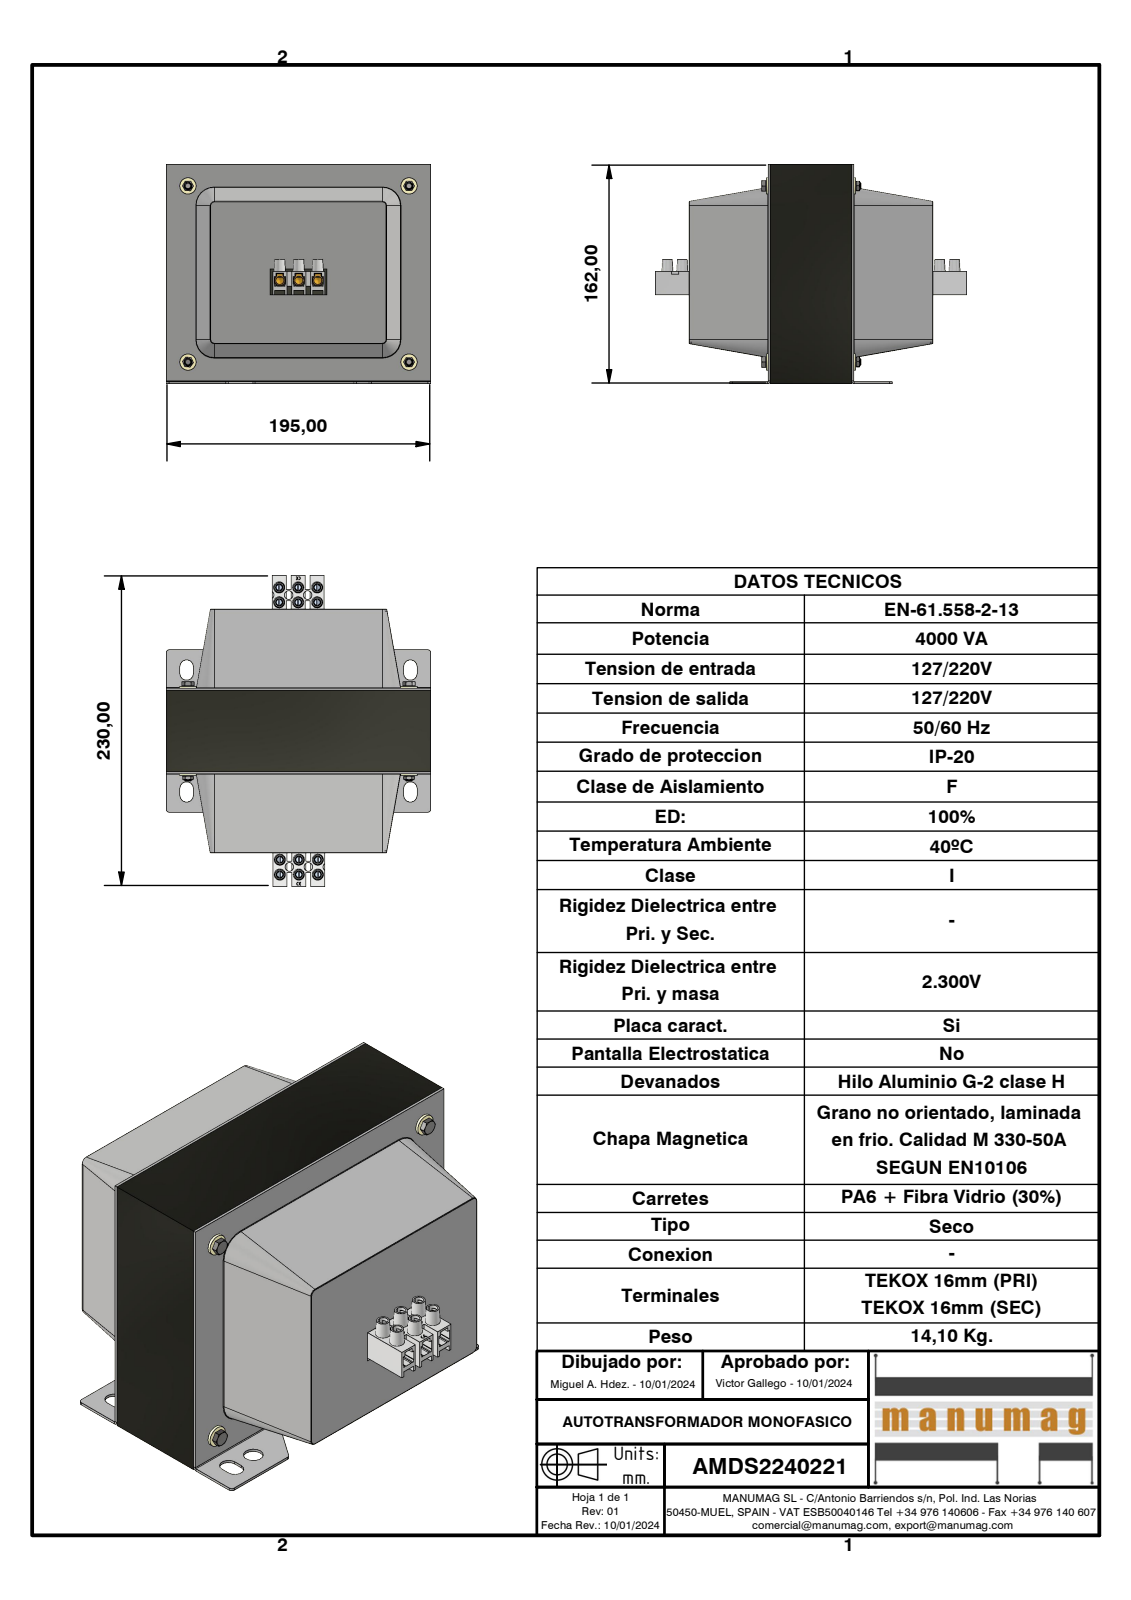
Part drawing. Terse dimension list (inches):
name: AMDS2240221; centrador M5; DIN 934 - M4 x 0,7; TAPA RC65 VENTANA 3 ELEMENTOS 16 (+8 more)
written by: Autodesk Inventor 2023 (AUTOMOTIVE_DESIGN)
unit: in
bodies: 51 solids, 2202 faces (1492 planar, 290 cylindrical, 420 other)
size: 9.055 × 7.677 × 6.378
volume: 98.68 in³; area: 629.1 in²
holes: 16× ⌀0.128, 12× ⌀0.217, 8× ⌀0.433, 6× ⌀0.236, 4× ⌀0.197, 4× ⌀0.248, 4× ⌀0.354
bosses: 12× ⌀0.157, 4× ⌀0.472, 4× ⌀0.264, 4× ⌀0.232, 4× ⌀0.18
rounds: 24× R0.108, 16× R0.015, 16× R0.032, 14× R0.079, 12× R0.118, 8× R0.032, 8× R0.197, 6× R0.004
face distances: 2.362, 0.059, 2.303, 4.724, 4.665, 2.244, 4.783, 5.118, 7.028, 2.421
hole spacings: 0.551, 0.346, 0.354, 0.701, 0.433, 1.102, 7.913, 0.853
